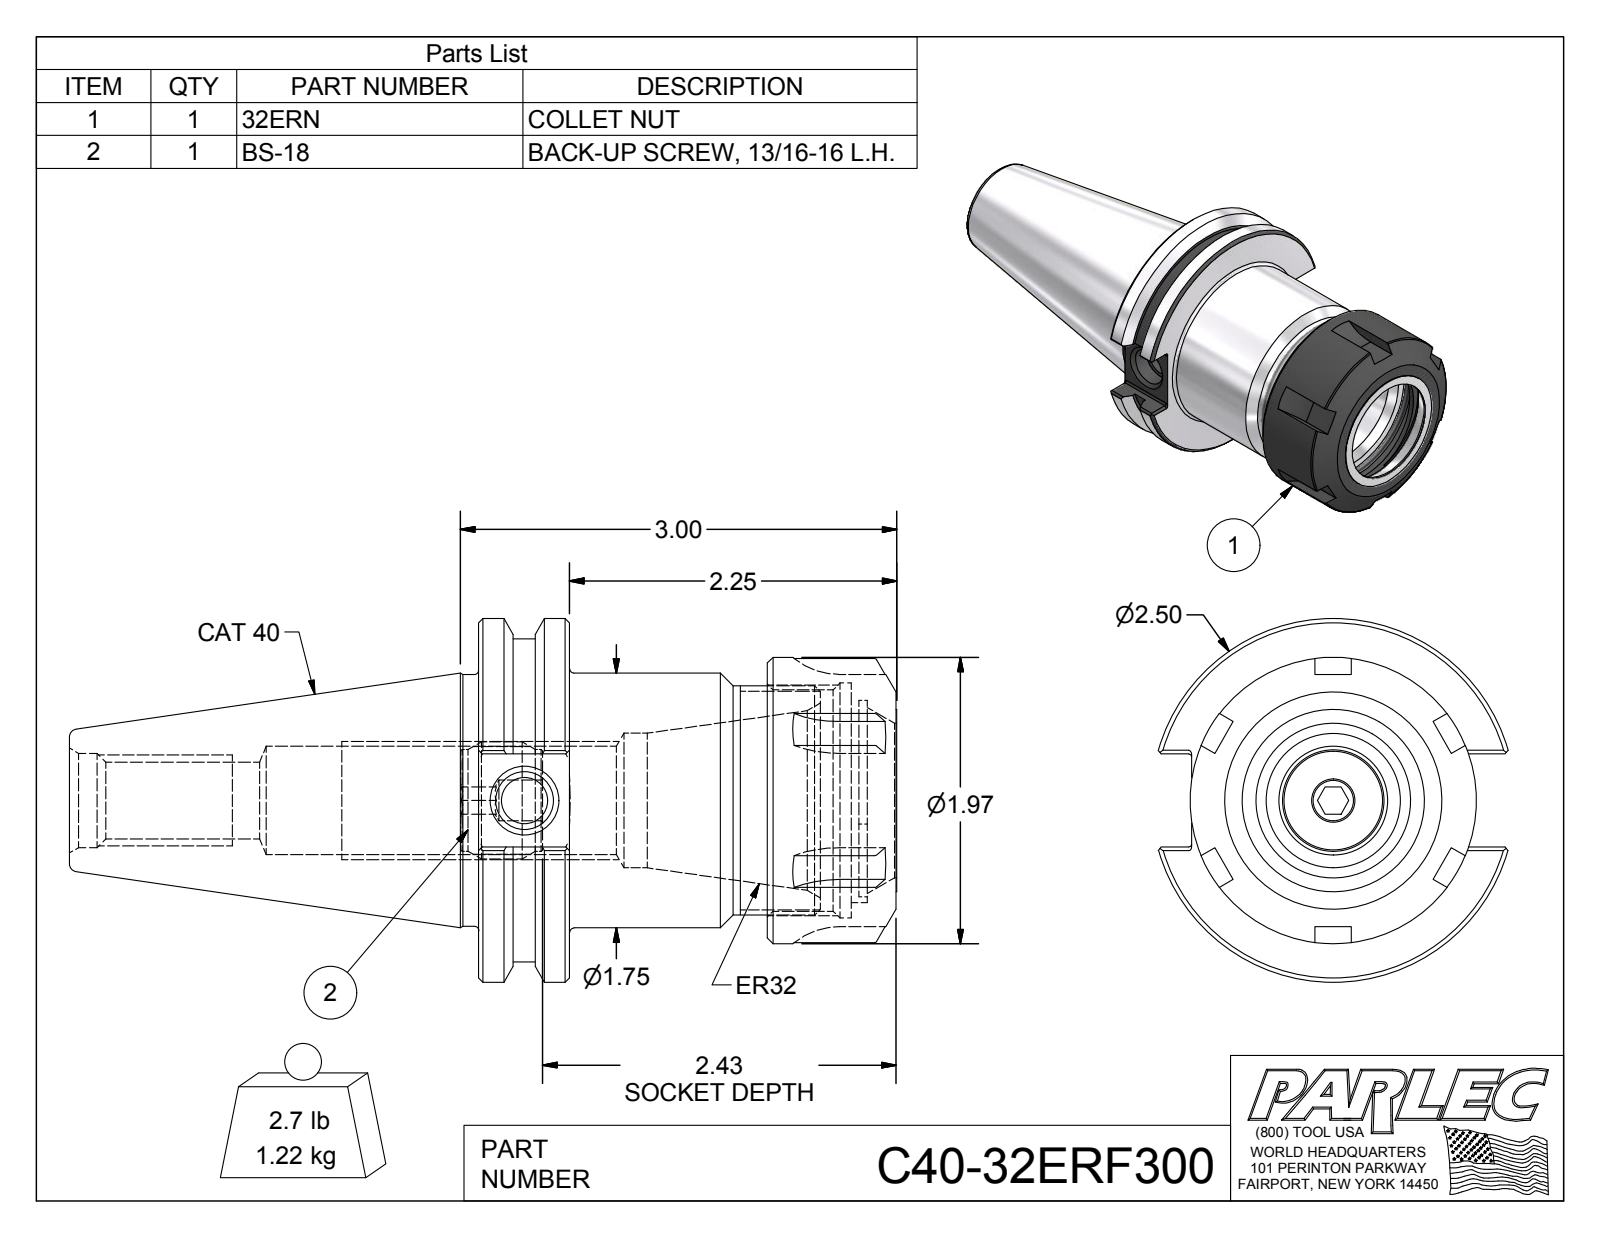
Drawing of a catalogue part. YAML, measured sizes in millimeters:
part_name: "C40-32ER3-1; 32ERN; BS-18; C40-32ERF300"
step_written_by: "Autodesk Inventor 2016 (AUTOMOTIVE_DESIGN)"
units: millimeters
bodies: {solids: 3, faces: 183, planar: 74, cylindrical: 50, other: 59}
overall_size: [144.46, 63.5, 61.05]
volume: 154859
surface_area: 40349
round_holes:
  - {diameter: 7.11, count: 1}
  - {diameter: 8, count: 1}
  - {diameter: 10.13, count: 1}
  - {diameter: 13.39, count: 1}
  - {diameter: 16.46, count: 1}
  - {diameter: 18.92, count: 1}
  - {diameter: 23.5, count: 1}
  - {diameter: 27, count: 1}
  - {diameter: 33.02, count: 1}
  - {diameter: 38.65, count: 1}
  - {diameter: 41, count: 1}
round_bosses_or_shafts:
  - {diameter: 63.5, count: 1}
  - {diameter: 56.36, count: 1}
  - {diameter: 50, count: 1}
  - {diameter: 44.45, count: 1}
  - {diameter: 43.94, count: 1}
  - {diameter: 40, count: 1}
  - {diameter: 20.45, count: 1}
  - {diameter: 17.78, count: 1}
partial_cylinders:
  - {radius: 0.51, count: 24}
  - {radius: 14.9, count: 1}
  - {radius: 17.5, count: 1}
face_to_face_distances: [15.88, 73.03, 57.15, 50.25, 34.37, 22.78, 65.26, 49.38, 15.01, 7.77]
hole_center_spacings: [1.86]
